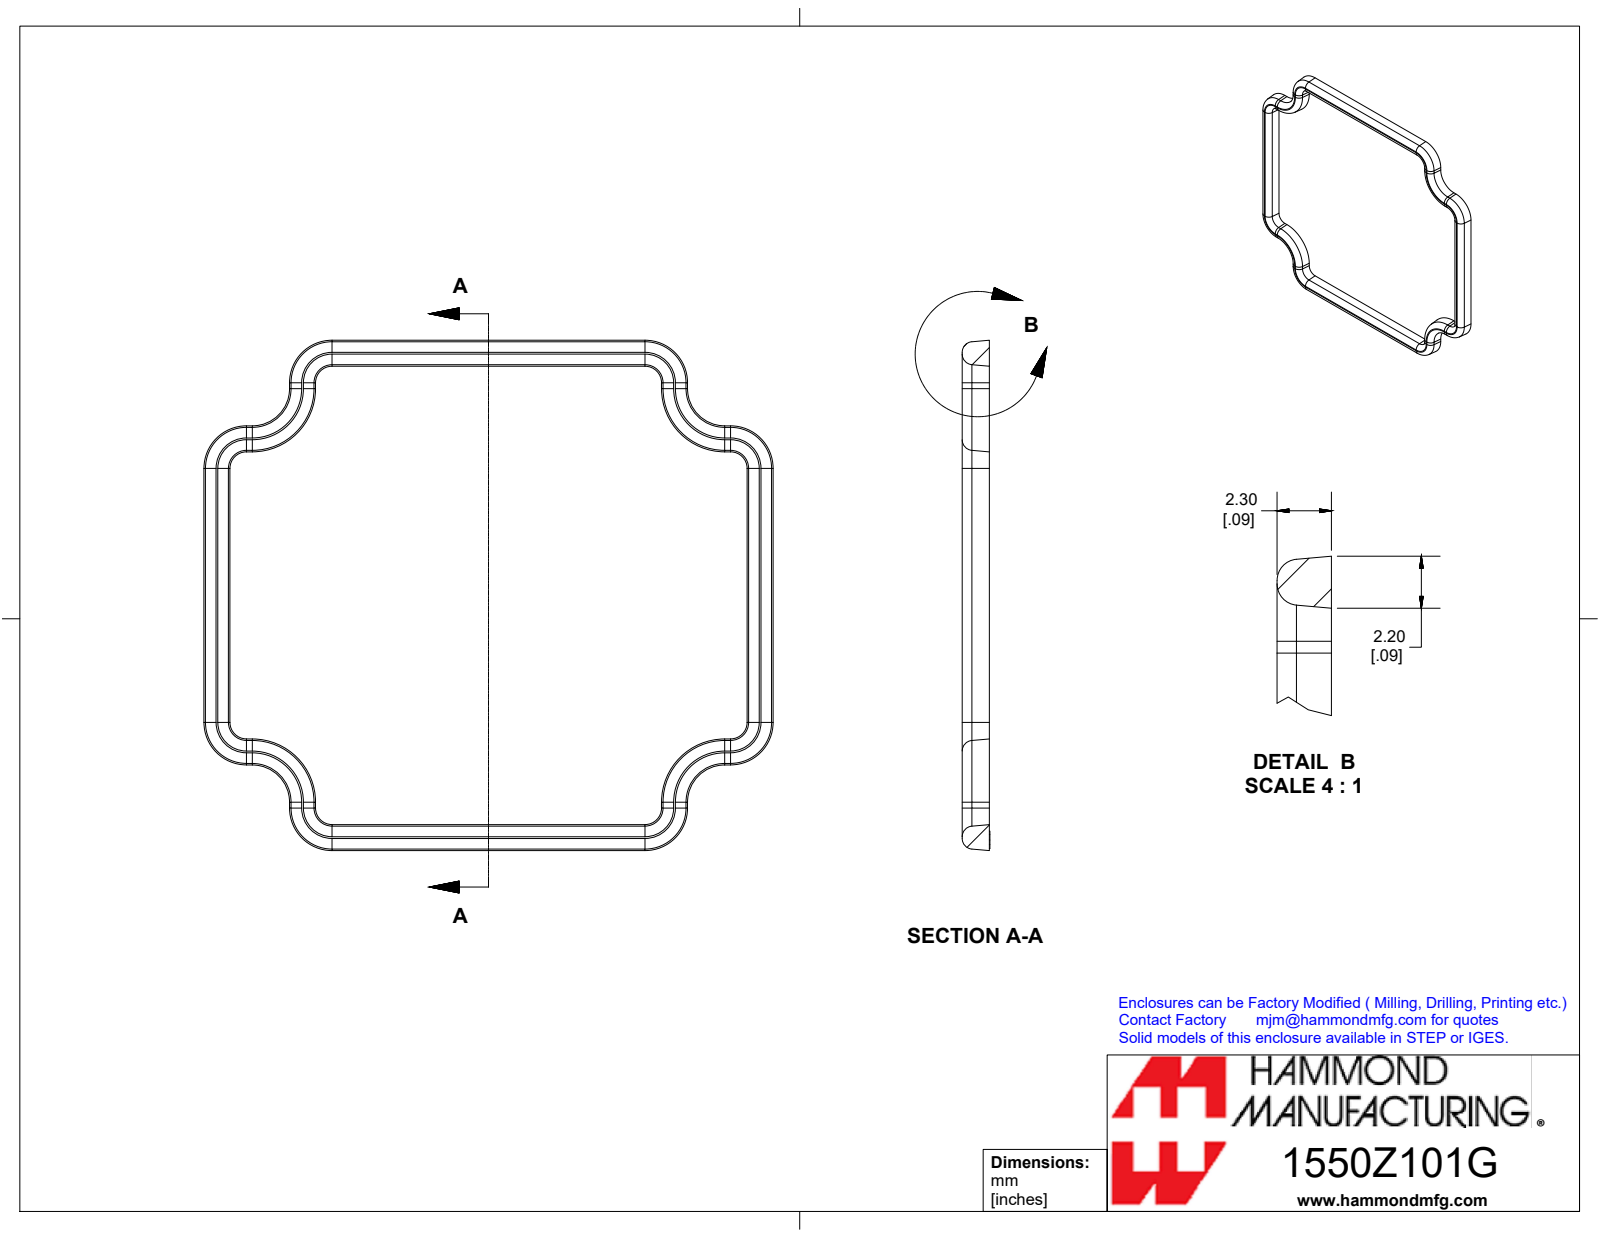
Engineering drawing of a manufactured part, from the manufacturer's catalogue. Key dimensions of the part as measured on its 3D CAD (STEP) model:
Part name (STEP PRODUCT): 1550Z101GASKET
STEP written by: SolidWorks 2019 (CONFIG_CONTROL_DESIGN)
Units: inches
Bodies: 1 solid, 147 faces (41 planar, 24 cylindrical, 82 other)
Overall size (bounding box): 1.898 × 1.701 × 0.093
Volume: 0.042 in³ · Surface area: 1.959 in²
Partial cylindrical surfaces — rounded edges, fillets, slot ends (radius × count): R0.035 ×16
Main face-to-face distances: 1.607, 1.804, 0.091, 0.284, 1.519, 1.323, 1.235, 1.039, 0.093, 0.134
